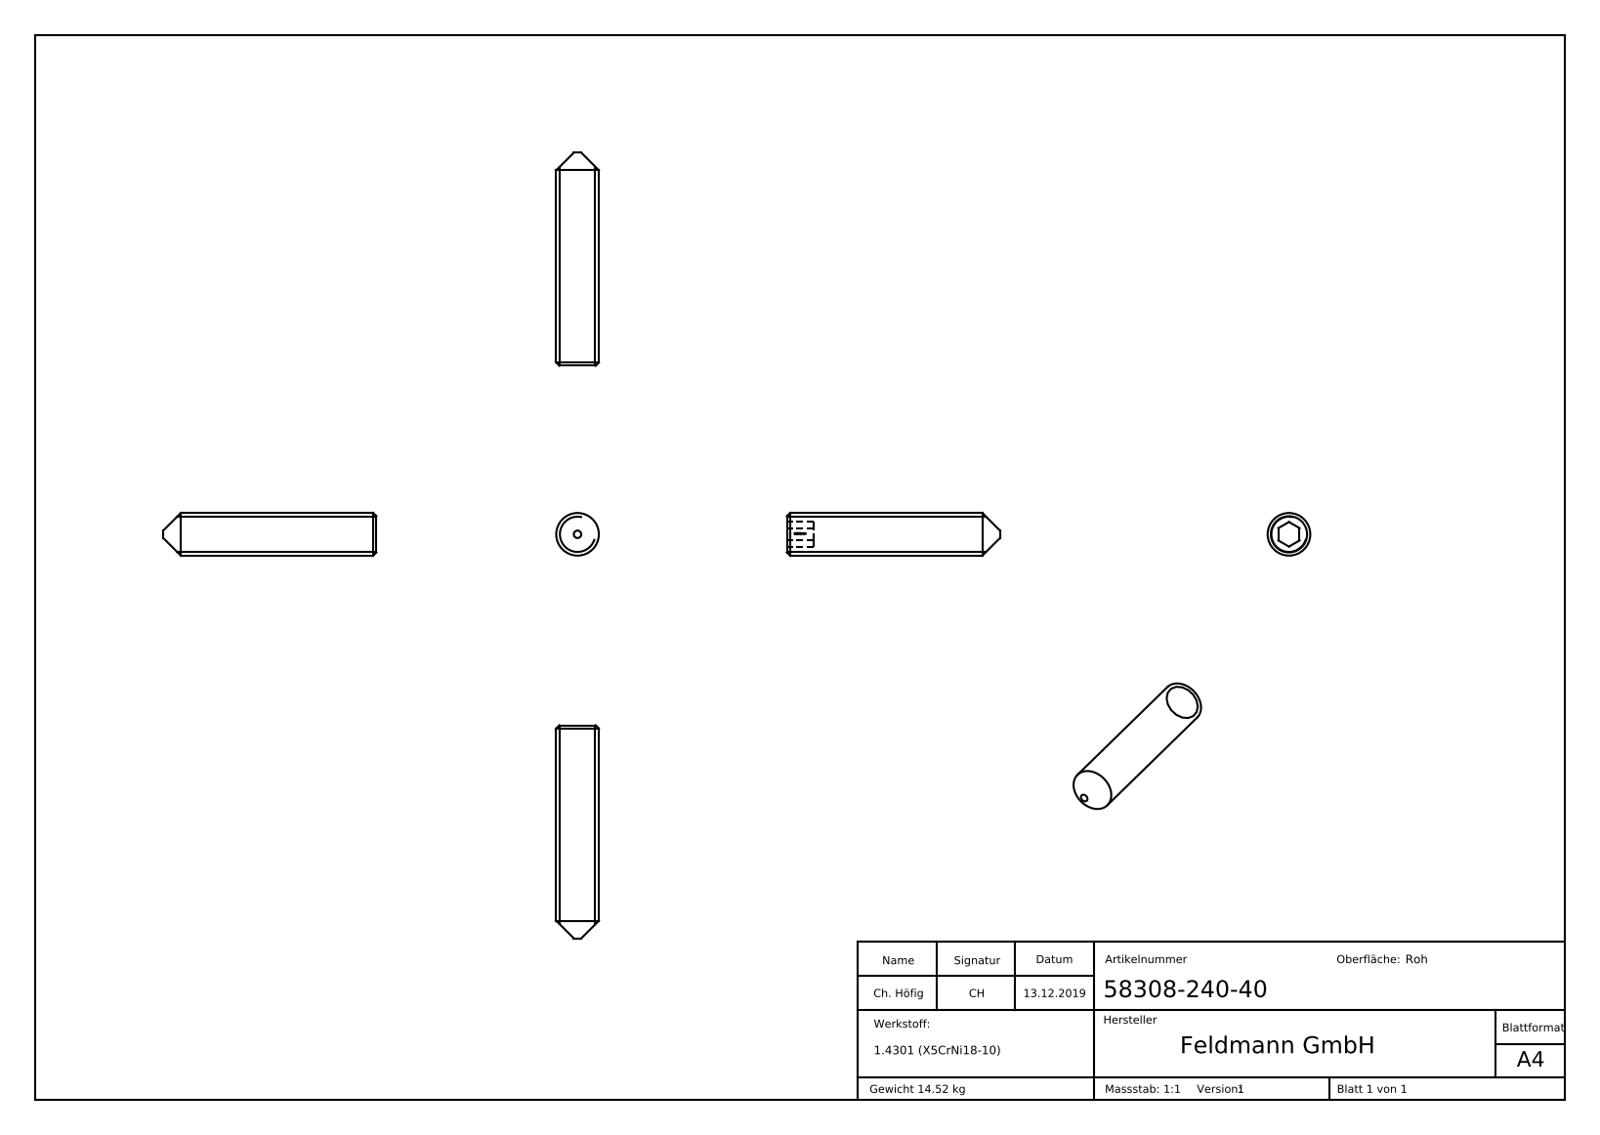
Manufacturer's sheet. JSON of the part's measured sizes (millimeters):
{"part_name": "58308-240-40", "step_written_by": "SolidWorks 2015 (CONFIG_CONTROL_DESIGN)", "units": "millimeters", "bodies": {"solids": 1, "faces": 177, "planar": 80, "cylindrical": 1, "other": 96}, "overall_size": [70, 8, 8], "volume_mm3": 1838, "surface_area_mm2": 1104, "round_bosses_or_shafts": [[8, 1]], "face_to_face_distances": [4, 5, 35, 40, 4.1, 0.41, 0.51, 1.64, 36.64, 37.15]}
